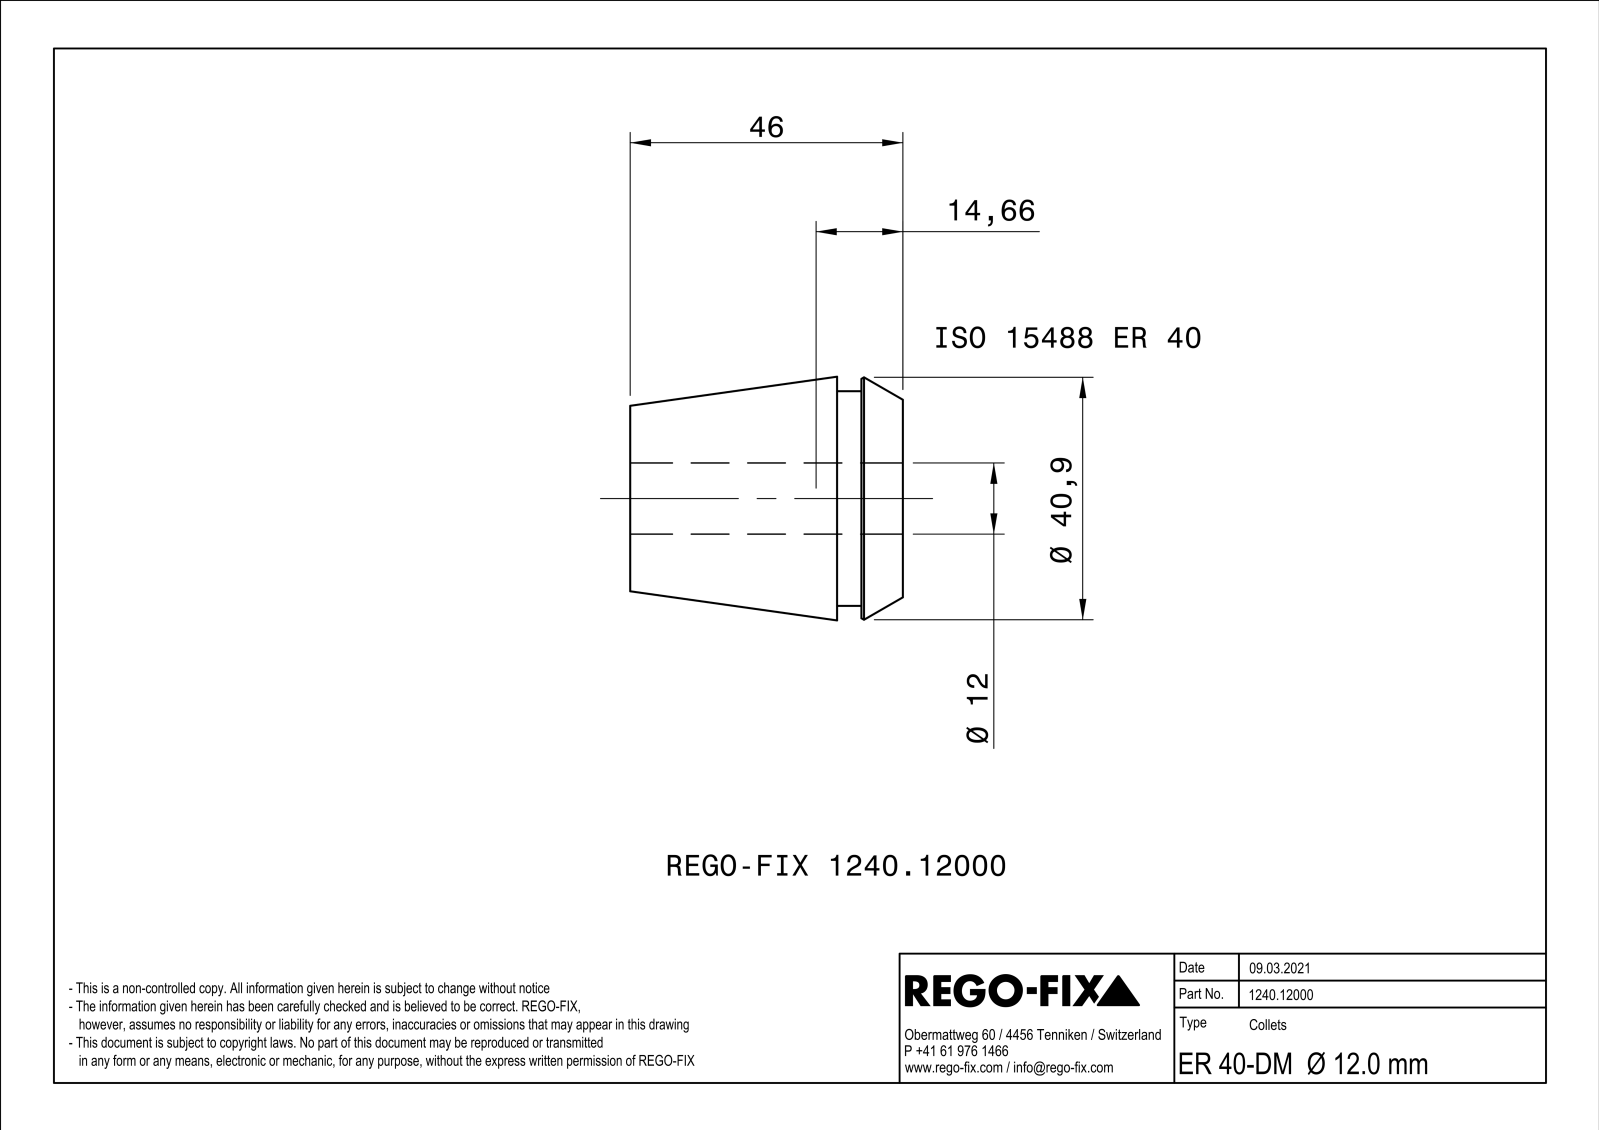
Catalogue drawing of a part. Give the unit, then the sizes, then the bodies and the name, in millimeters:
Units: millimetres
Overall size (bounding box): 46 × 40.99 × 40.99
Round holes (diameter × count): ⌀12 ×1
Round bosses / shafts (diameter × count): ⌀36.2 ×1
Main face-to-face distances: 1, 46, 11.1, 34.9, 7, 4.1, 39, 17, 10, 5.9
Volume: 35 862 mm³ · Surface area: 21 474 mm²
Bodies: 1 solid, 154 faces (80 planar, 9 cylindrical, 65 other)
Part name (STEP PRODUCT): NOCUT
STEP written by: SIEMENS PLM Software Solid Edge ST10 (AUTOMOTIVE_DESIGN)
